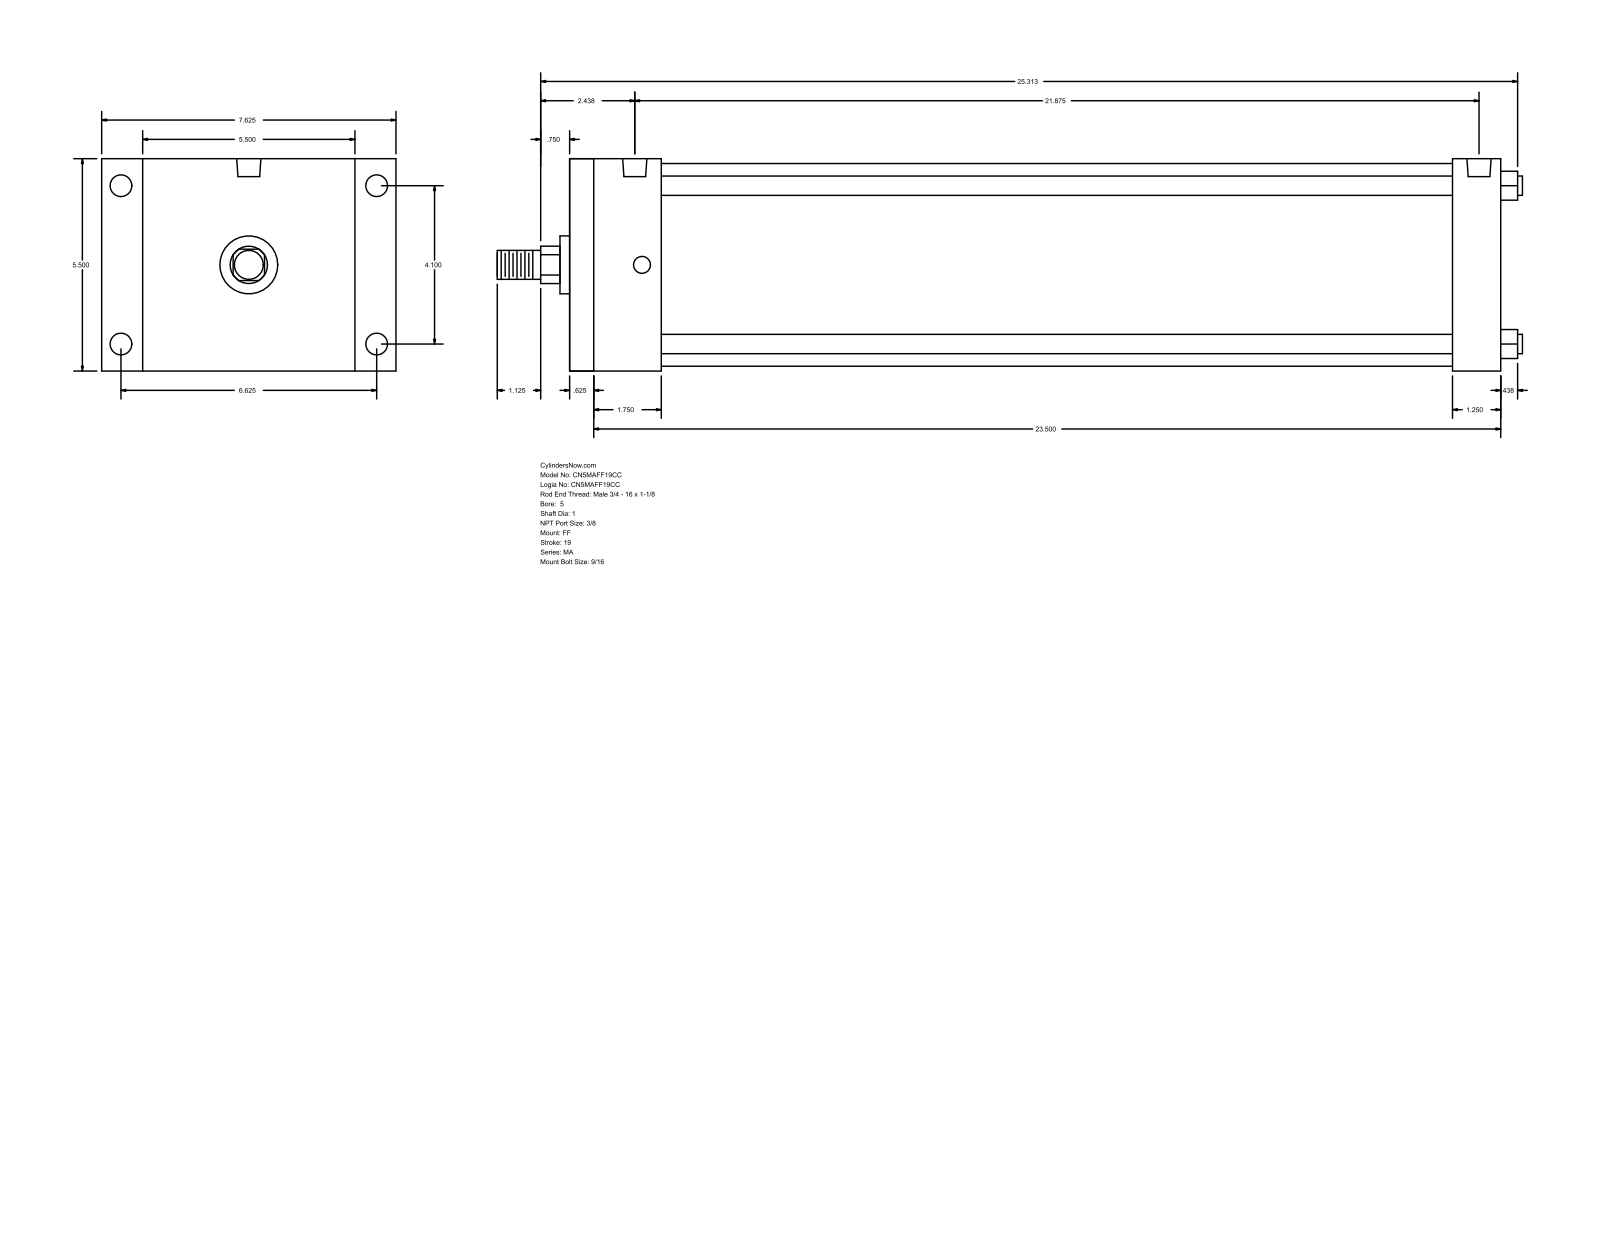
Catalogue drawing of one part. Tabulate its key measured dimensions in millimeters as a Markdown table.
| quantity | value |
| --- | --- |
| part name | MA_FF__0500_1 |
| STEP written by | GSSL Pune (CONFIG_CONTROL_DESIGN) |
| units | millimeters |
| bodies | 0 solids, 92 faces (64 planar, 28 cylindrical, 0 other) |
| overall size | 674.69 × 193.68 × 139.7 |
| round holes (diameter × count) | 11.11 × 4, 14.29 × 4, 15.93 × 2 |
| round bosses / shafts (diameter × count) | 12.7 × 4, 133.35 × 1, 38.1 × 1, 25.4 × 1, 19.05 × 1 |
| partial cylindrical surfaces (radius × count) | 12.29 × 1 |
| main face-to-face distances | 139.7, 612.78, 15.87, 596.91, 581.03, 565.16, 31.75, 60.33, 44.46, 520.7 |
| hole center spacings | 104.14, 168.28, 197.9, 546.1, 4.76, 4.77, 550.86, 550.87 |
